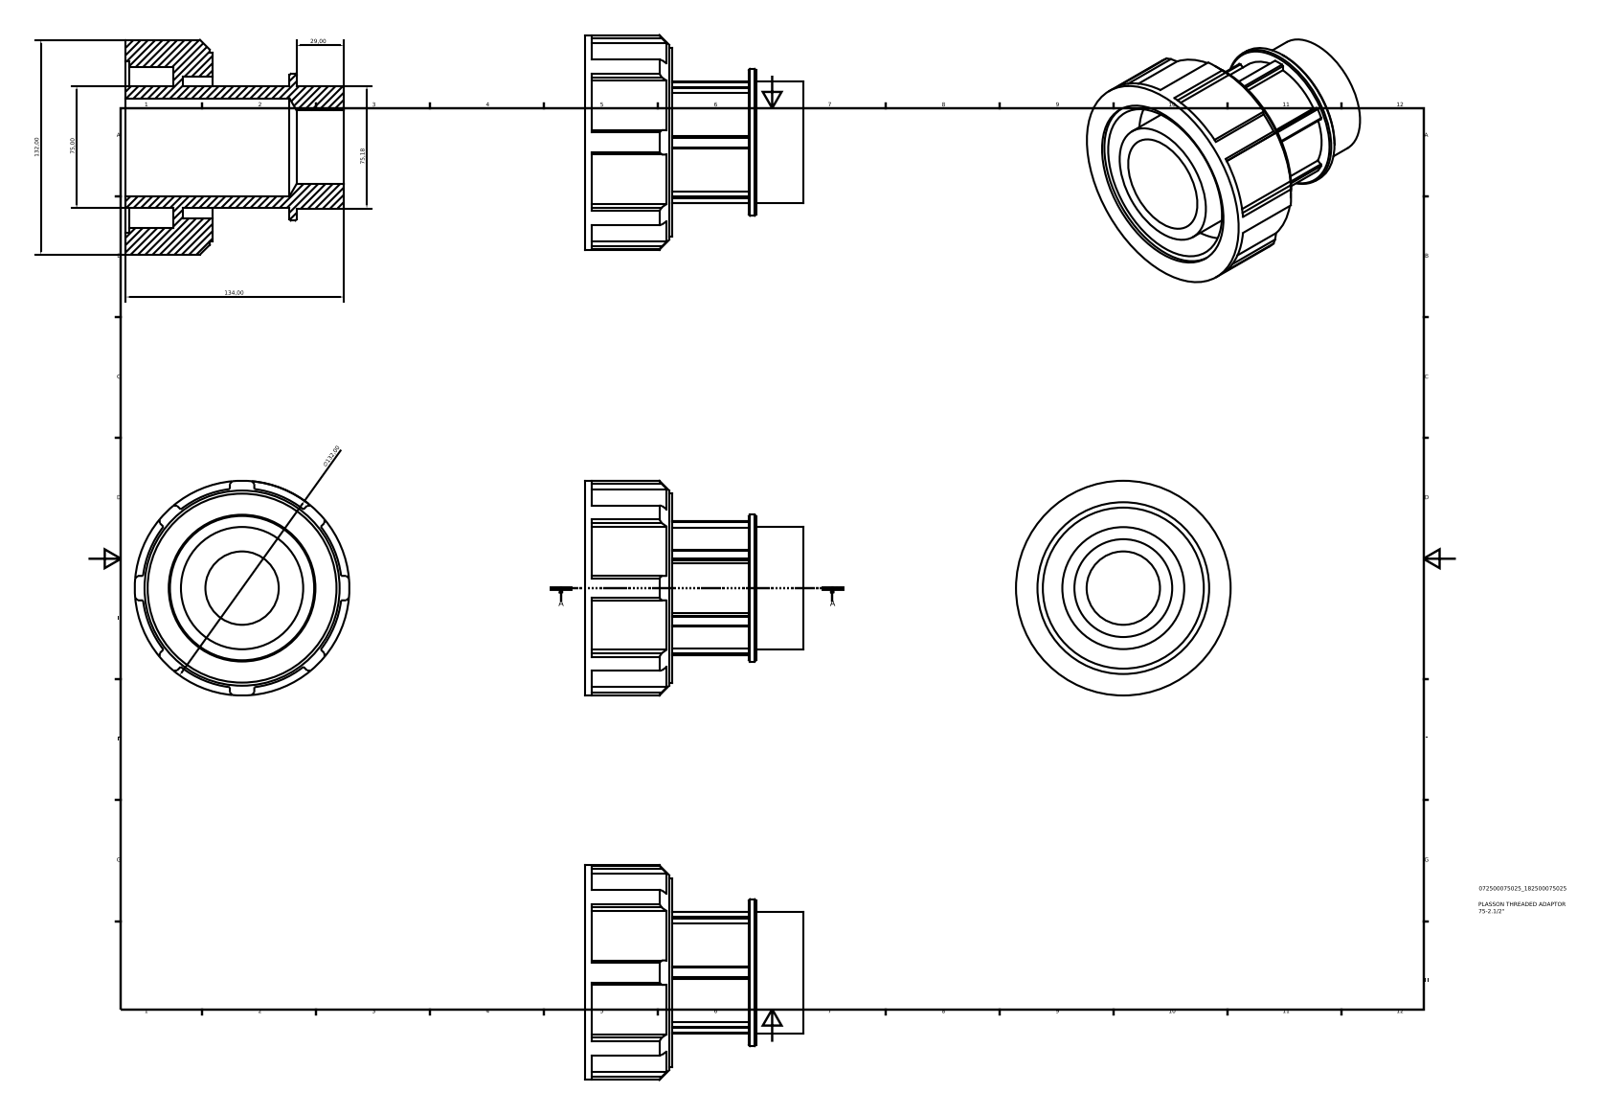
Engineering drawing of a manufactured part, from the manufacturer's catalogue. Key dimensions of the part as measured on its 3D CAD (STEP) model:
Part name (STEP PRODUCT): 072500075025
STEP written by: Autodesk Inventor 2015 (AUTOMOTIVE_DESIGN)
Units: millimetres
Bodies: 1 solid, 108 faces (74 planar, 30 cylindrical, 4 other)
Overall size (bounding box): 134 × 132 × 132
Volume: 570 012 mm³ · Surface area: 121 007 mm²
Round holes (diameter × count): ⌀45.11 ×1, ⌀60.15 ×1, ⌀87 ×1, ⌀99 ×1, ⌀105.6 ×1
Round bosses / shafts (diameter × count): ⌀132 ×1, ⌀116.16 ×1, ⌀90.22 ×1, ⌀75.18 ×1, ⌀75 ×1
Partial cylindrical surfaces — rounded edges, fillets, slot ends (radius × count): R41.25 ×1, R61.38 ×1
Main face-to-face distances: 29, 53.6, 105, 24.6, 134, 80.4, 2.01, 49.58, 51.59, 76
